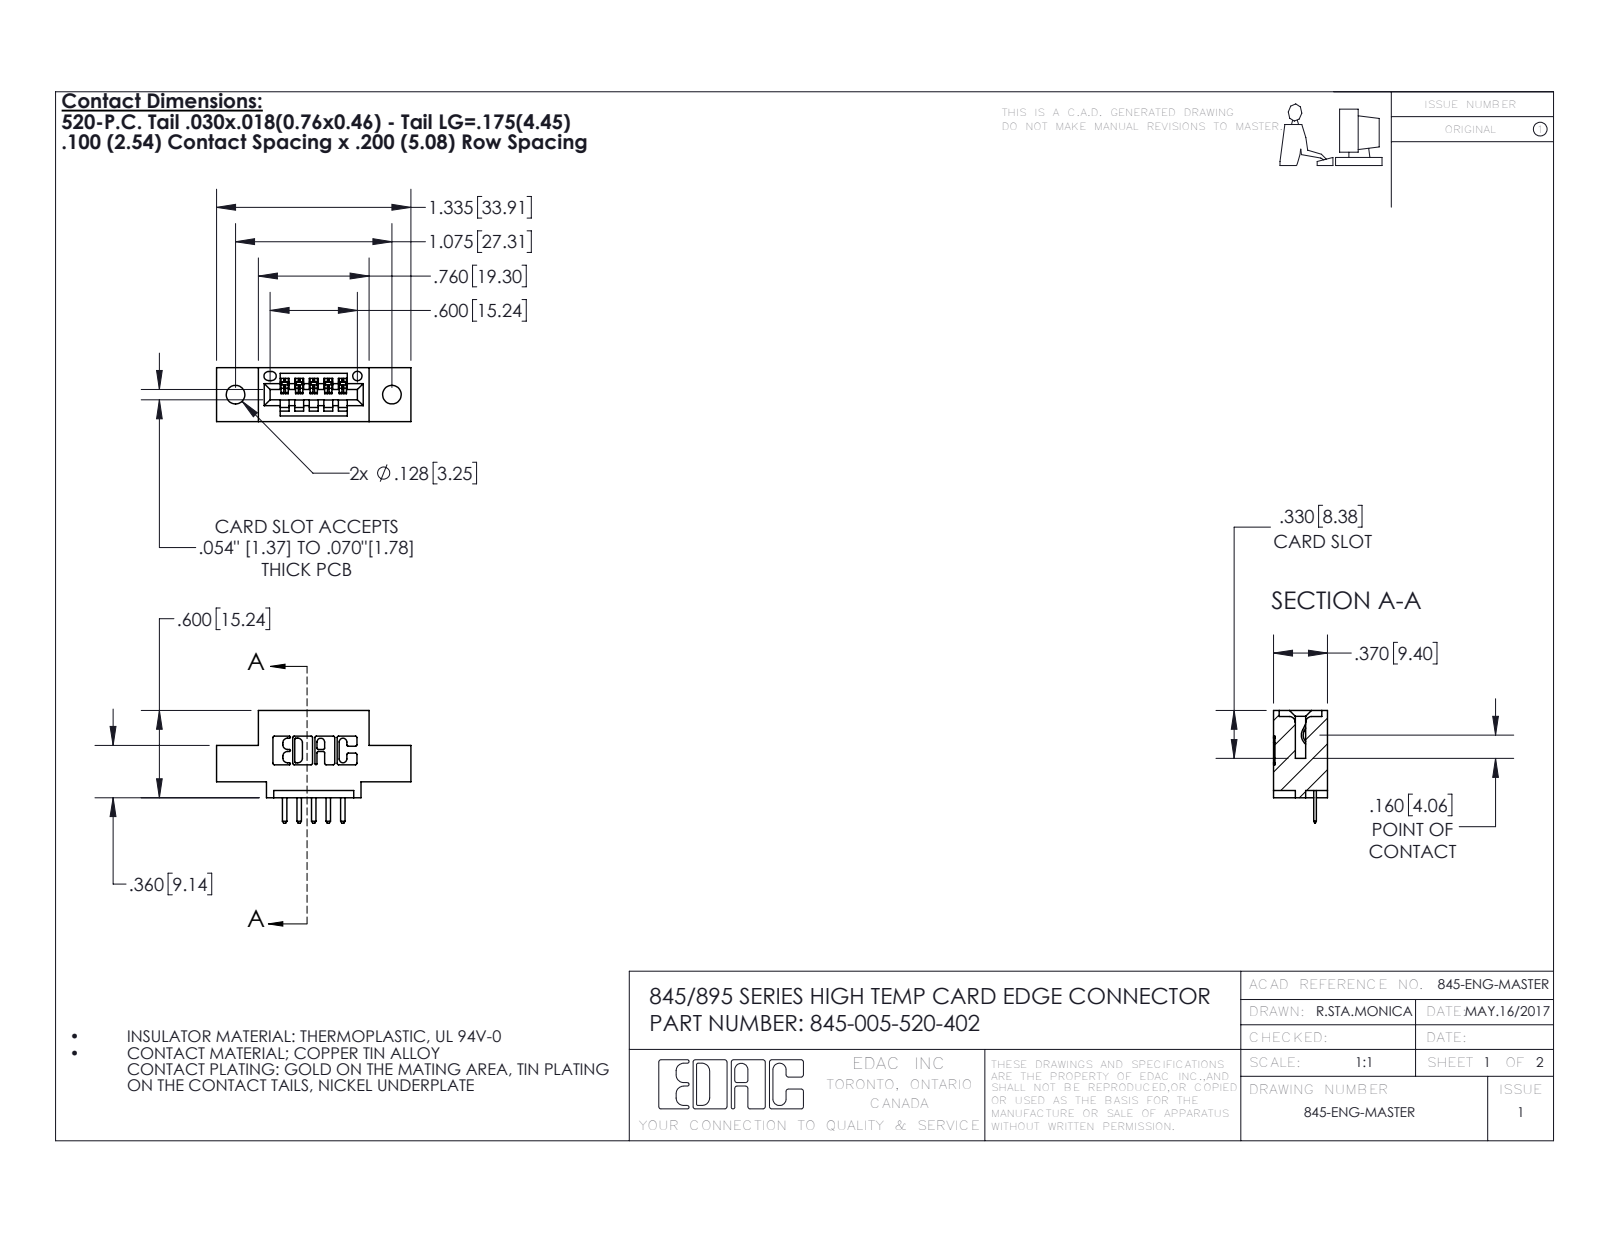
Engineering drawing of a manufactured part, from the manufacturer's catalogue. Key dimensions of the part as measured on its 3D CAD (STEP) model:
Part name (STEP PRODUCT): 345 Part_0.110 Offset - 0.128 Dia; 345-005-520-402; 345-292-001_345-293-120
STEP written by: SolidWorks 2016 (CONFIG_CONTROL_DESIGN)
Units: inches
Bodies: 6 solids, 440 faces (294 planar, 146 cylindrical, 0 other)
Overall size (bounding box): 1.335 × 0.775 × 0.37
Volume: 0.17 in³ · Surface area: 4.607 in²
Round holes (diameter × count): ⌀0.128 ×2, ⌀0.064 ×1
Partial cylindrical surfaces — rounded edges, fillets, slot ends (radius × count): R0.01 ×22, R0.01 ×12, R0.006 ×10, R0.007 ×6, R0.031 ×6, R0.026 ×3, R0.031 ×2, R0.04 ×2
Main face-to-face distances: 0.37, 0.2, 0.1, 0.298, 0.072, 0.25, 0.025, 0.06, 0.16, 0.55
Hole centre spacings: 0.27, 0.847, 1.075
